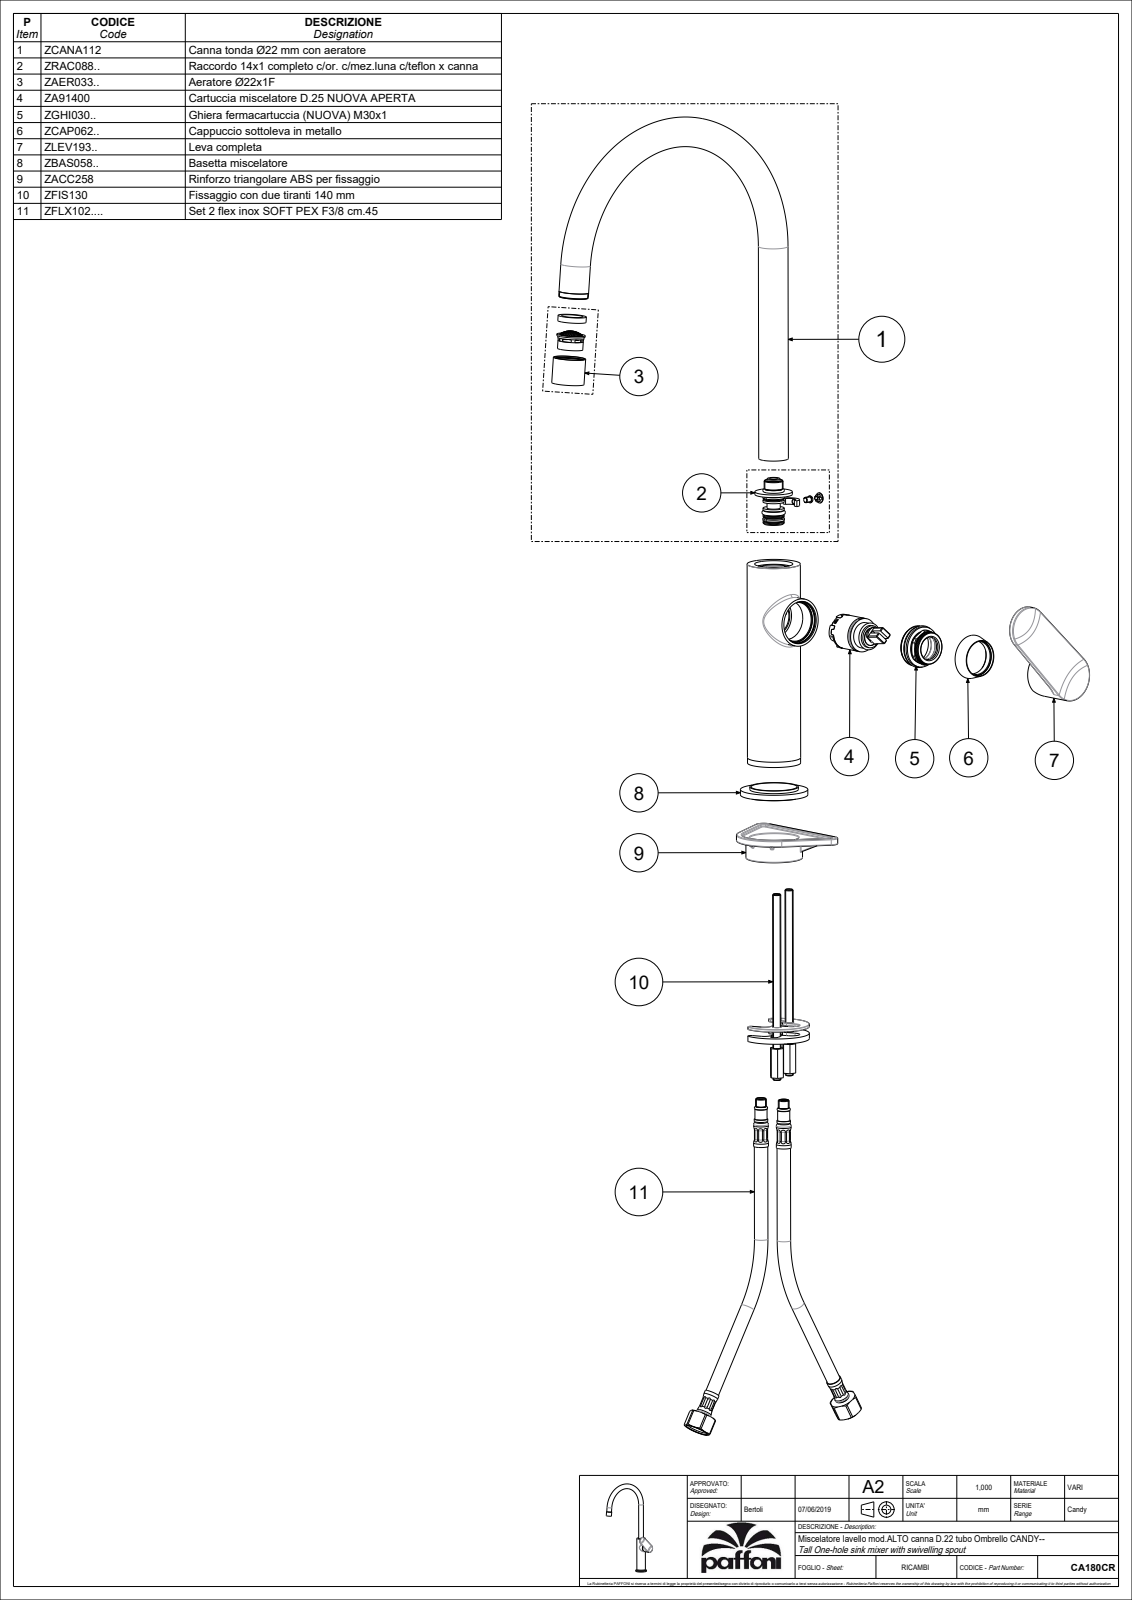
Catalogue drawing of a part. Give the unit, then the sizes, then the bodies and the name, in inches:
Units: inches
Overall size (bounding box): 16.594 × 9.211 × 3.457
Round holes (diameter × count): ⌀0.217 ×3, ⌀0.126 ×2, ⌀0.197 ×2, ⌀0.276 ×2, ⌀0.339 ×2, ⌀0.37 ×2, ⌀0.118 ×1, ⌀0.157 ×1, ⌀0.177 ×1, ⌀0.236 ×1, ⌀0.591 ×1, ⌀0.63 ×1
Round bosses / shafts (diameter × count): ⌀0.866 ×2, ⌀1.969 ×1, ⌀1.555 ×1, ⌀1.551 ×1, ⌀1.417 ×1, ⌀1.398 ×1, ⌀1.378 ×1, ⌀0.945 ×1
Partial cylindrical surfaces — rounded edges, fillets, slot ends (radius × count): R0.118 ×4, R0.138 ×1, R0.63 ×1, R0.774 ×1
Main face-to-face distances: 6.061, 0.157, 6.063, 0.156, 5.906, 2.244, 2.243, 2.087, 3.819, 0.02
Hole centre spacings: 0.265, 0.352, 0.368, 0.513, 0.609, 0.374, 0.406, 0.414
Volume: 20.25 in³ · Surface area: 142.7 in²
Bodies: 2 solids, 284 faces (66 planar, 117 cylindrical, 101 other)
Part name (STEP PRODUCT): CA180CR
STEP written by: CREO PARAMETRIC BY PTC INC, 2020044 (CONFIG_CONTROL_DESIGN)
